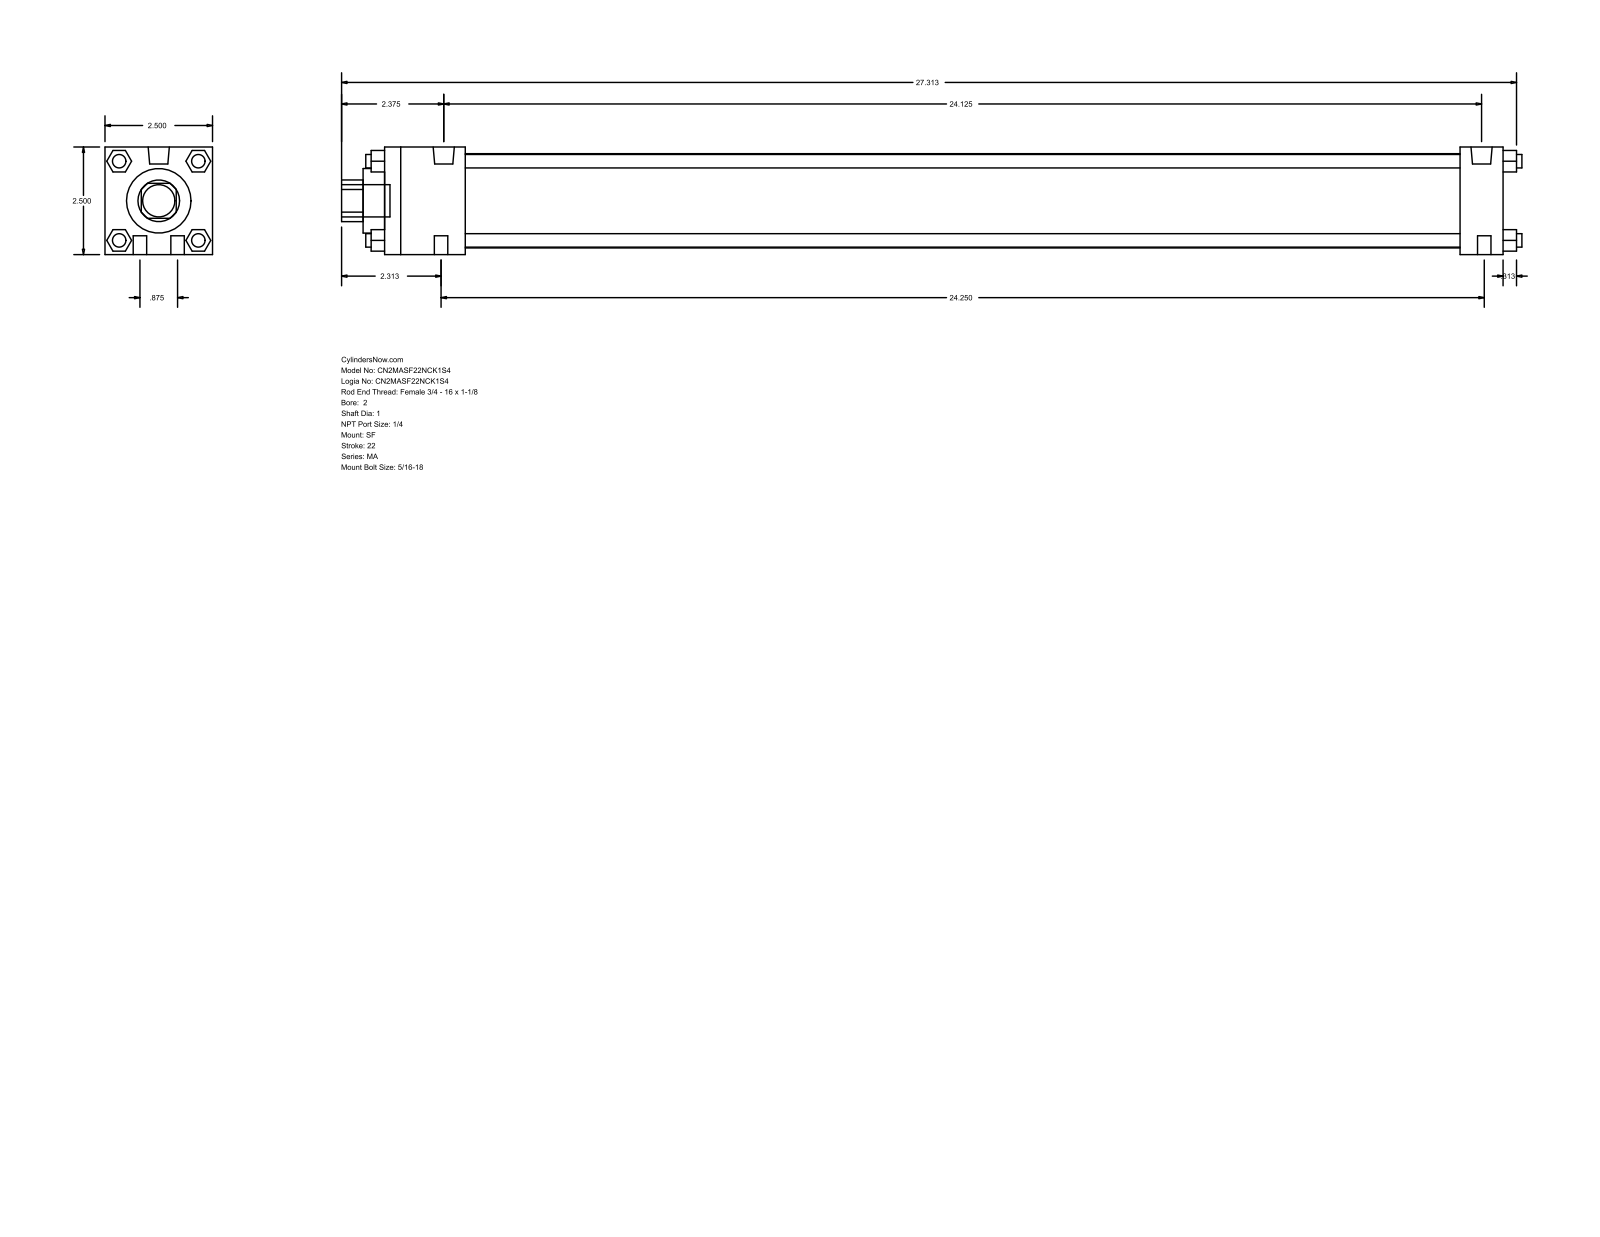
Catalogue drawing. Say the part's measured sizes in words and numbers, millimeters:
The part is named "MA_SF__0200_1". Its 3-D file was written by "GSSL Pune (CONFIG_CONTROL_DESIGN)". It is 0 solids with 124 faces: 94 planar, 30 cylindrical and 0 other. Overall it measures 696.91 by 63.5 by 63.5 millimeters. Round holes: 1 of diameter 25.4, 1 of diameter 38.1, 1 of diameter 55.63. Round bosses or shafts: 10 of diameter 7.94, 2 of diameter 12.49, 1 of diameter 19.05. Partial cylindrical surfaces (rounded edges, fillets, slot ends): 1 of radius 12.29. The main face-to-face distances are 63.5, 660.4, 12.7, 25.4, 635, 47.63, 587.37, 612.77, 23.37, 40.47.
